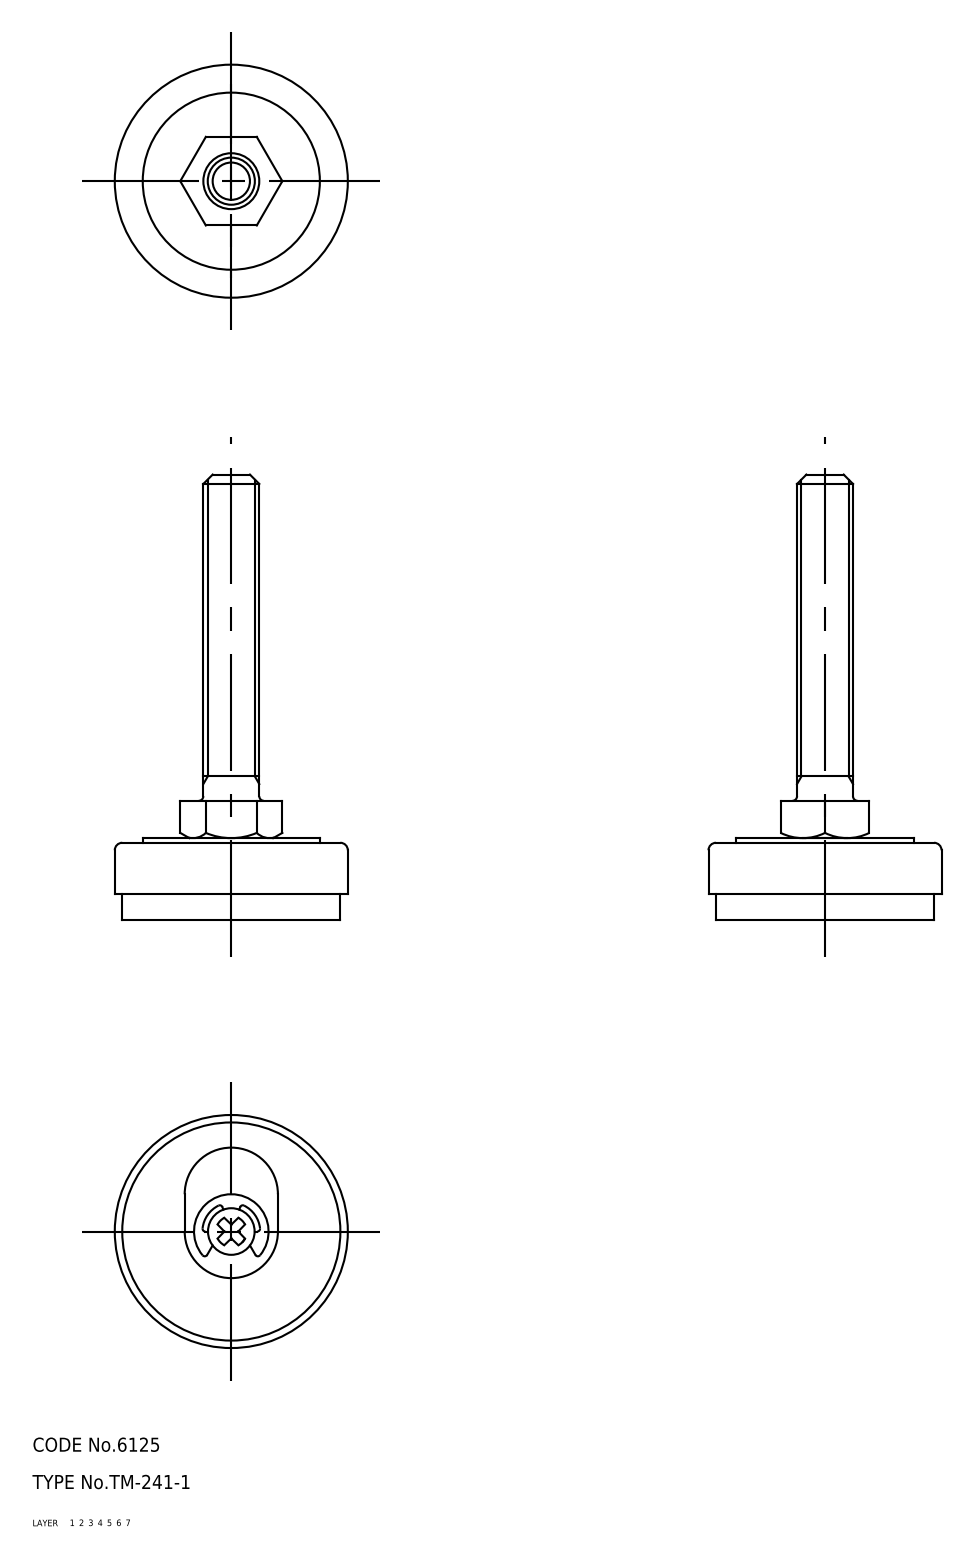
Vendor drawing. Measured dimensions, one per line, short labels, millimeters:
name: washer; rubber pad; retainer; cover (+3 more)
written by: CADfix (AUTOMOTIVE_DESIGN)
unit: mm
bodies: 6 solids, 115 faces (0 planar, 0 cylindrical, 115 other)
size: 95.5 × 50 × 50
volume: 39 096 mm³; area: 24 136 mm²
